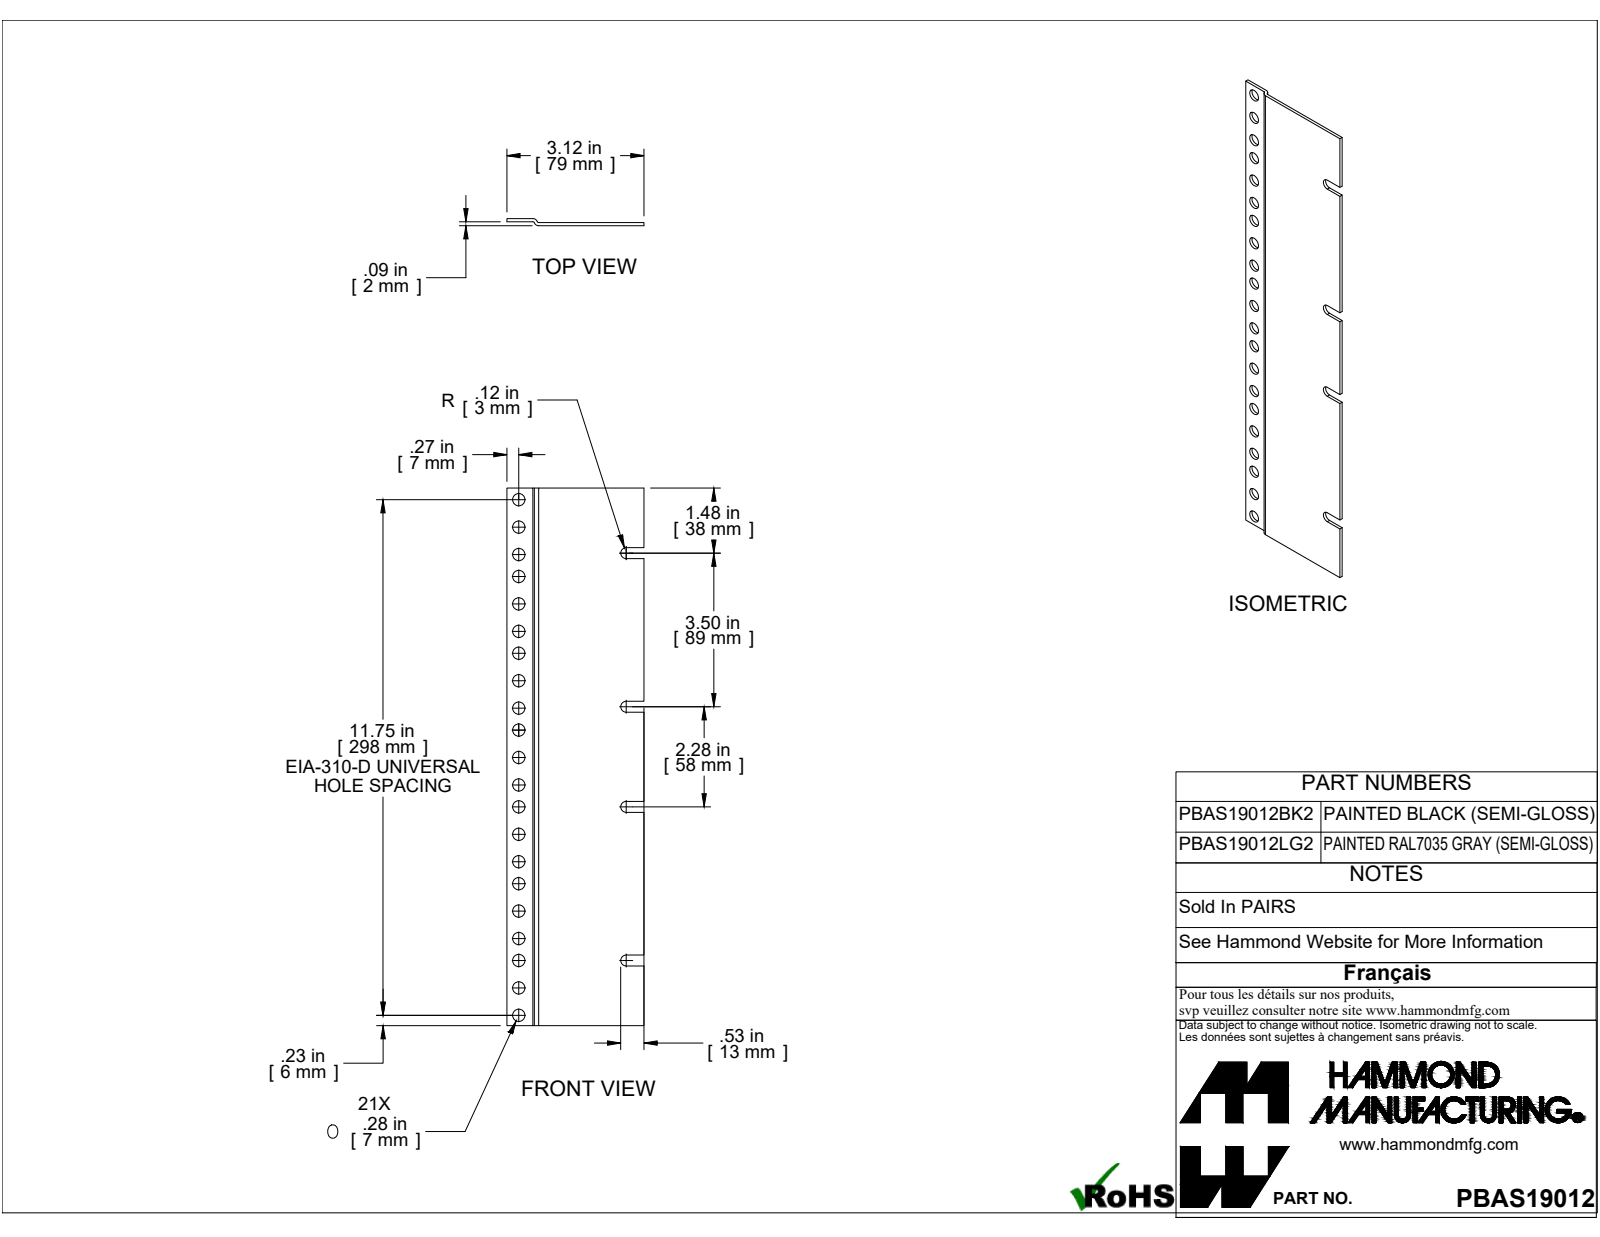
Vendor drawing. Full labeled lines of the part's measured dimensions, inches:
Part name (STEP PRODUCT): PBAS19012LG2
STEP written by: SolidWorks 2019 (CONFIG_CONTROL_DESIGN)
Units: inches
Bodies: 1 solid, 49 faces (20 planar, 29 cylindrical, 0 other)
Overall size (bounding box): 12.25 × 3.125 × 0.162
Volume: 2.659 in³ · Surface area: 77.69 in²
Round holes (diameter × count): ⌀0.281 ×21
Partial cylindrical surfaces — rounded edges, fillets, slot ends (radius × count): R0.125 ×4, R0.036 ×2, R0.108 ×2
Main face-to-face distances: 0.072, 0.09, 0.162, 0.018, 0.09, 0.072, 3.125, 12.25, 3.5, 0.25
Hole centre spacings: 1.75, 3.5, 5.25, 7, 0.625, 0.625, 1.25, 0.5
